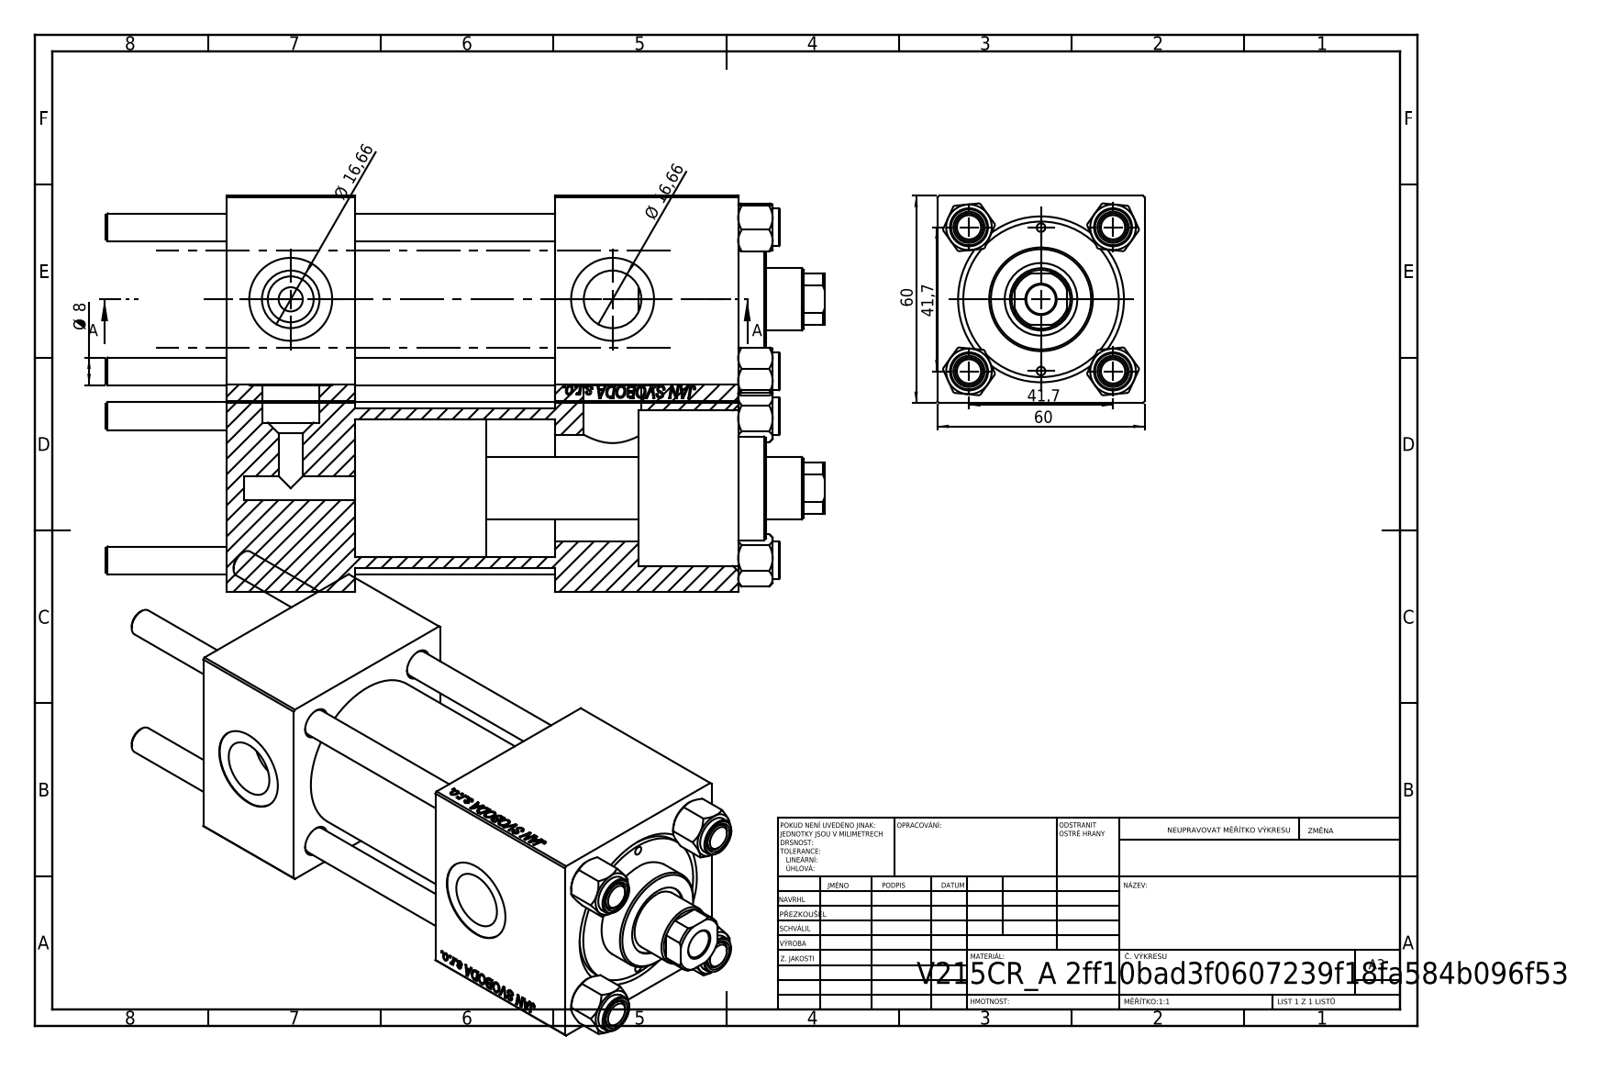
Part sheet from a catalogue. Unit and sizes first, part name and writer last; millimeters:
Units: millimetres
Overall size (bounding box): 208 × 60 × 60
Round holes (diameter × count): ⌀8 ×4, ⌀2.5 ×2, ⌀7 ×2, ⌀16.66 ×2, ⌀24 ×2, ⌀8.5 ×1, ⌀18 ×1, ⌀21 ×1, ⌀31 ×1, ⌀40 ×1, ⌀45 ×1
Round bosses / shafts (diameter × count): ⌀11 ×4, ⌀46 ×1, ⌀30 ×1
Partial cylindrical surfaces — rounded edges, fillets, slot ends (radius × count): R8.5 ×1
Main face-to-face distances: 60, 37, 148, 111, 58, 53, 95, 119.3, 82.3, 24.3
Hole centre spacings: 20.85, 29.49, 41.7, 46.53, 20.75, 58.97, 41.5, 93.16
Volume: 413 503 mm³ · Surface area: 114 082 mm²
Bodies: 11 solids, 1139 faces (520 planar, 83 cylindrical, 536 other)
Part name (STEP PRODUCT): V215CR_BODY_A; V215_VC_A; NUT_M5; CR025_012_A_0_G_A_G_M_020_+#_##_TYCINKA (+1 more)
STEP written by: SolidWorks 2019 (CONFIG_CONTROL_DESIGN)
